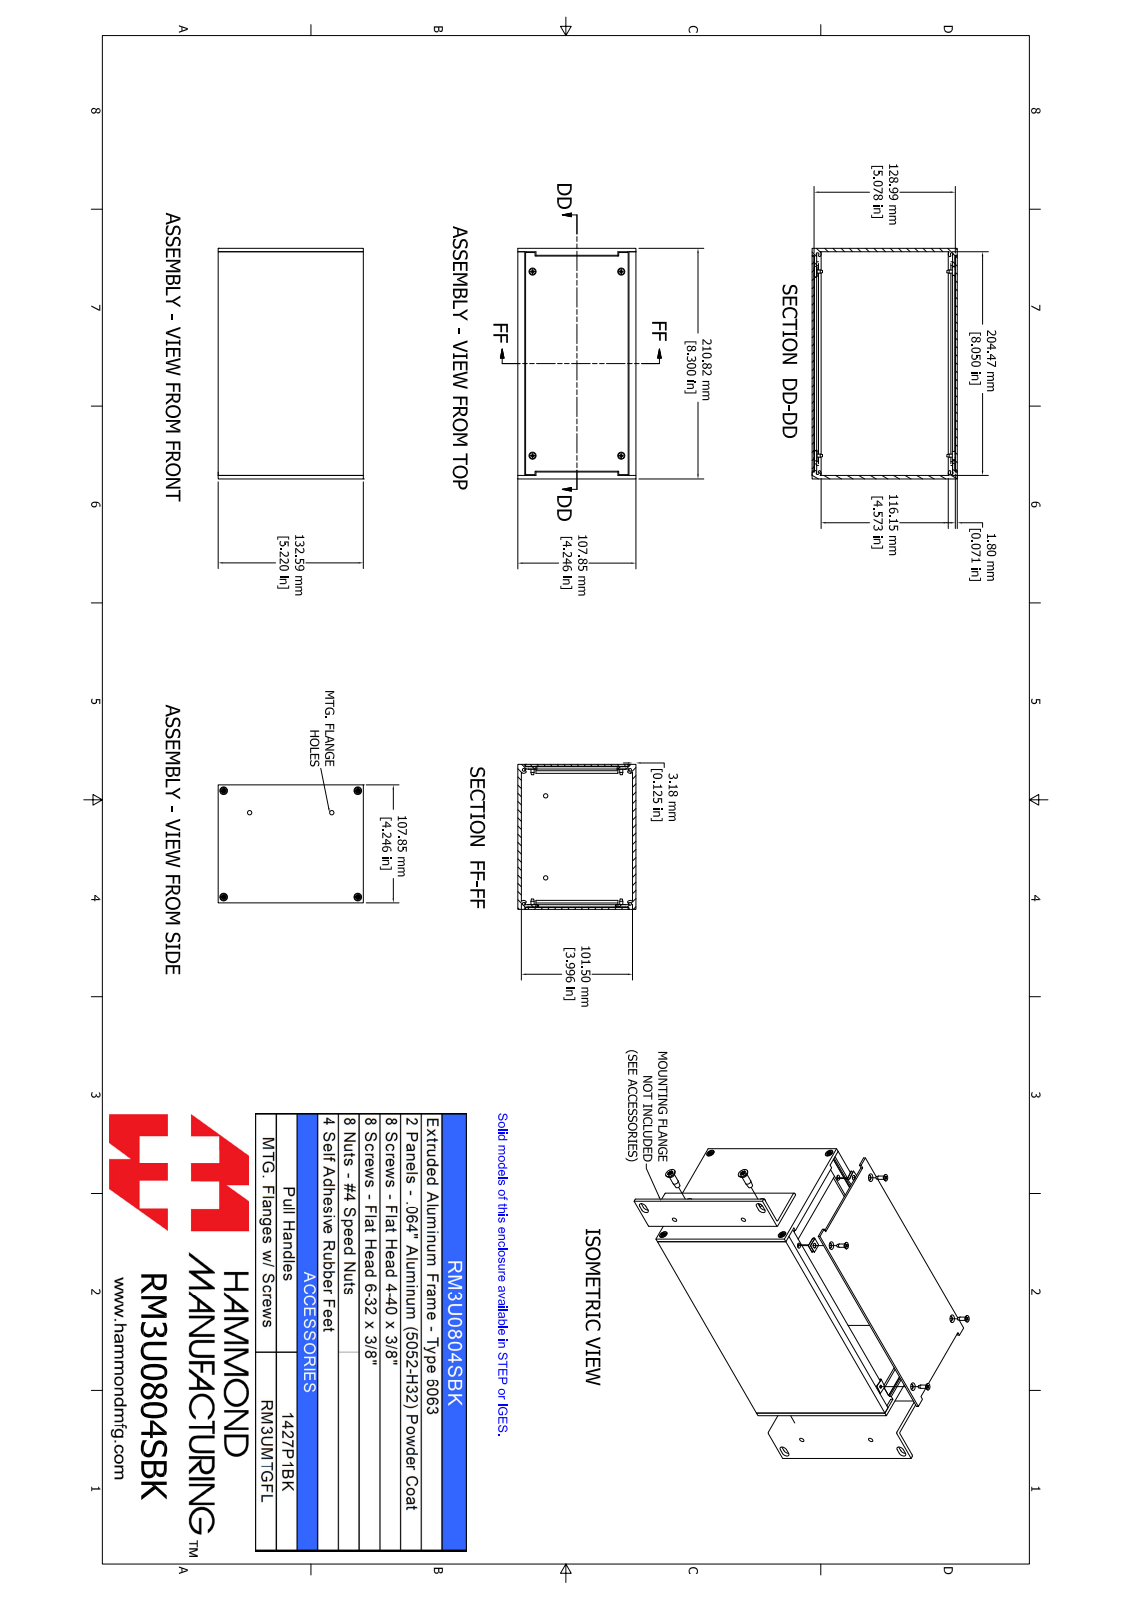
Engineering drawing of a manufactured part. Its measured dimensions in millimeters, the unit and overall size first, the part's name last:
Units: millimetres
Overall size (bounding box): 210.8 × 132.6 × 107.8
Round holes (diameter × count): ⌀2.5 ×4, ⌀3.5 ×4, ⌀4 ×4, ⌀4.3 ×4, ⌀4 ×2
Round bosses / shafts (diameter × count): ⌀6 ×4, ⌀5.4 ×4, ⌀3.5 ×4, ⌀2.8 ×4
Partial cylindrical surfaces — rounded edges, fillets, slot ends (radius × count): R0.9 ×8, R1 ×8, R1.2 ×8, R1.3 ×8, R3.2 ×8, R1 ×4
Main face-to-face distances: 3.2, 3.2, 1.8, 130.8, 107.8, 101.5, 104.7, 104.7, 132.6, 129
Hole centre spacings: 81.1, 97.2, 122.5, 125.3, 156.4, 168.3, 186.8, 31.1
Volume: 379 700 mm³ · Surface area: 293 100 mm²
Bodies: 30 solids, 804 faces (396 planar, 120 cylindrical, 288 other)
Part name (STEP PRODUCT): RM3U0804SBK
STEP written by: SolidWorks 2021 (AUTOMOTIVE_DESIGN)
